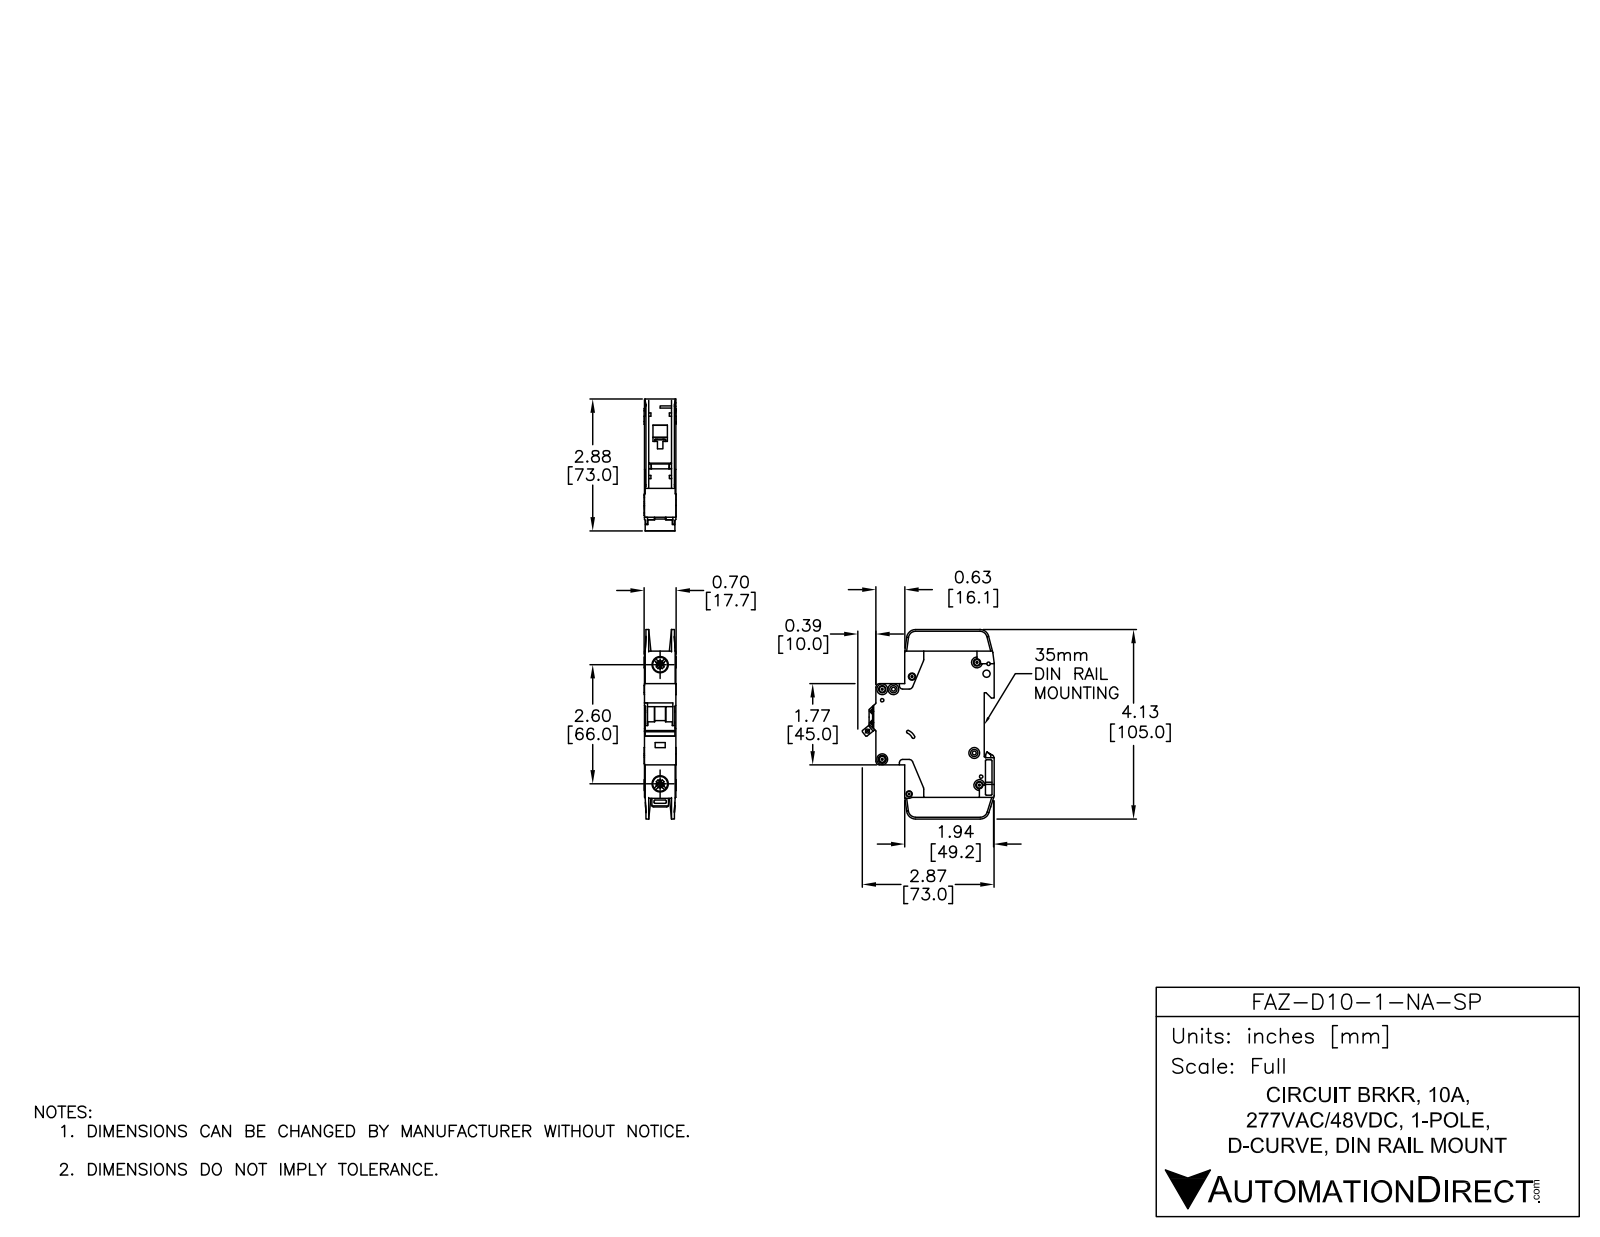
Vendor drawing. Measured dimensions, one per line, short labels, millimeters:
name: FAZ-D10-1-NA-SP
written by: SolidWorks 2014 (AUTOMOTIVE_DESIGN)
unit: mm
bodies: 3 solids, 784 faces (409 planar, 263 cylindrical, 112 other)
size: 105 × 73.04 × 17.7
volume: 77 695 mm³; area: 24 740 mm²
holes: 7× ⌀3.6, 2× ⌀1.09, 2× ⌀1.5, 2× ⌀4, 2× ⌀7.15, 2× ⌀8.2, 1× ⌀1.9, 1× ⌀2.15, 1× ⌀2.2, 1× ⌀2.55, 1× ⌀3.3, 1× ⌀3.4
bosses: 7× ⌀6, 1× ⌀2.5
rounds: 29× R0.25, 18× R0.5, 10× R1, 10× R2, 5× R5, 4× R4, 3× R1.8, 2× R0.2
face distances: 17.5, 15.05, 0.7, 2.45, 1.75, 15.75, 13.3, 14, 12.6, 2
hole spacings: 6.2, 5.19, 6.1, 8.19, 8.56, 8.7, 11.11, 12.45
